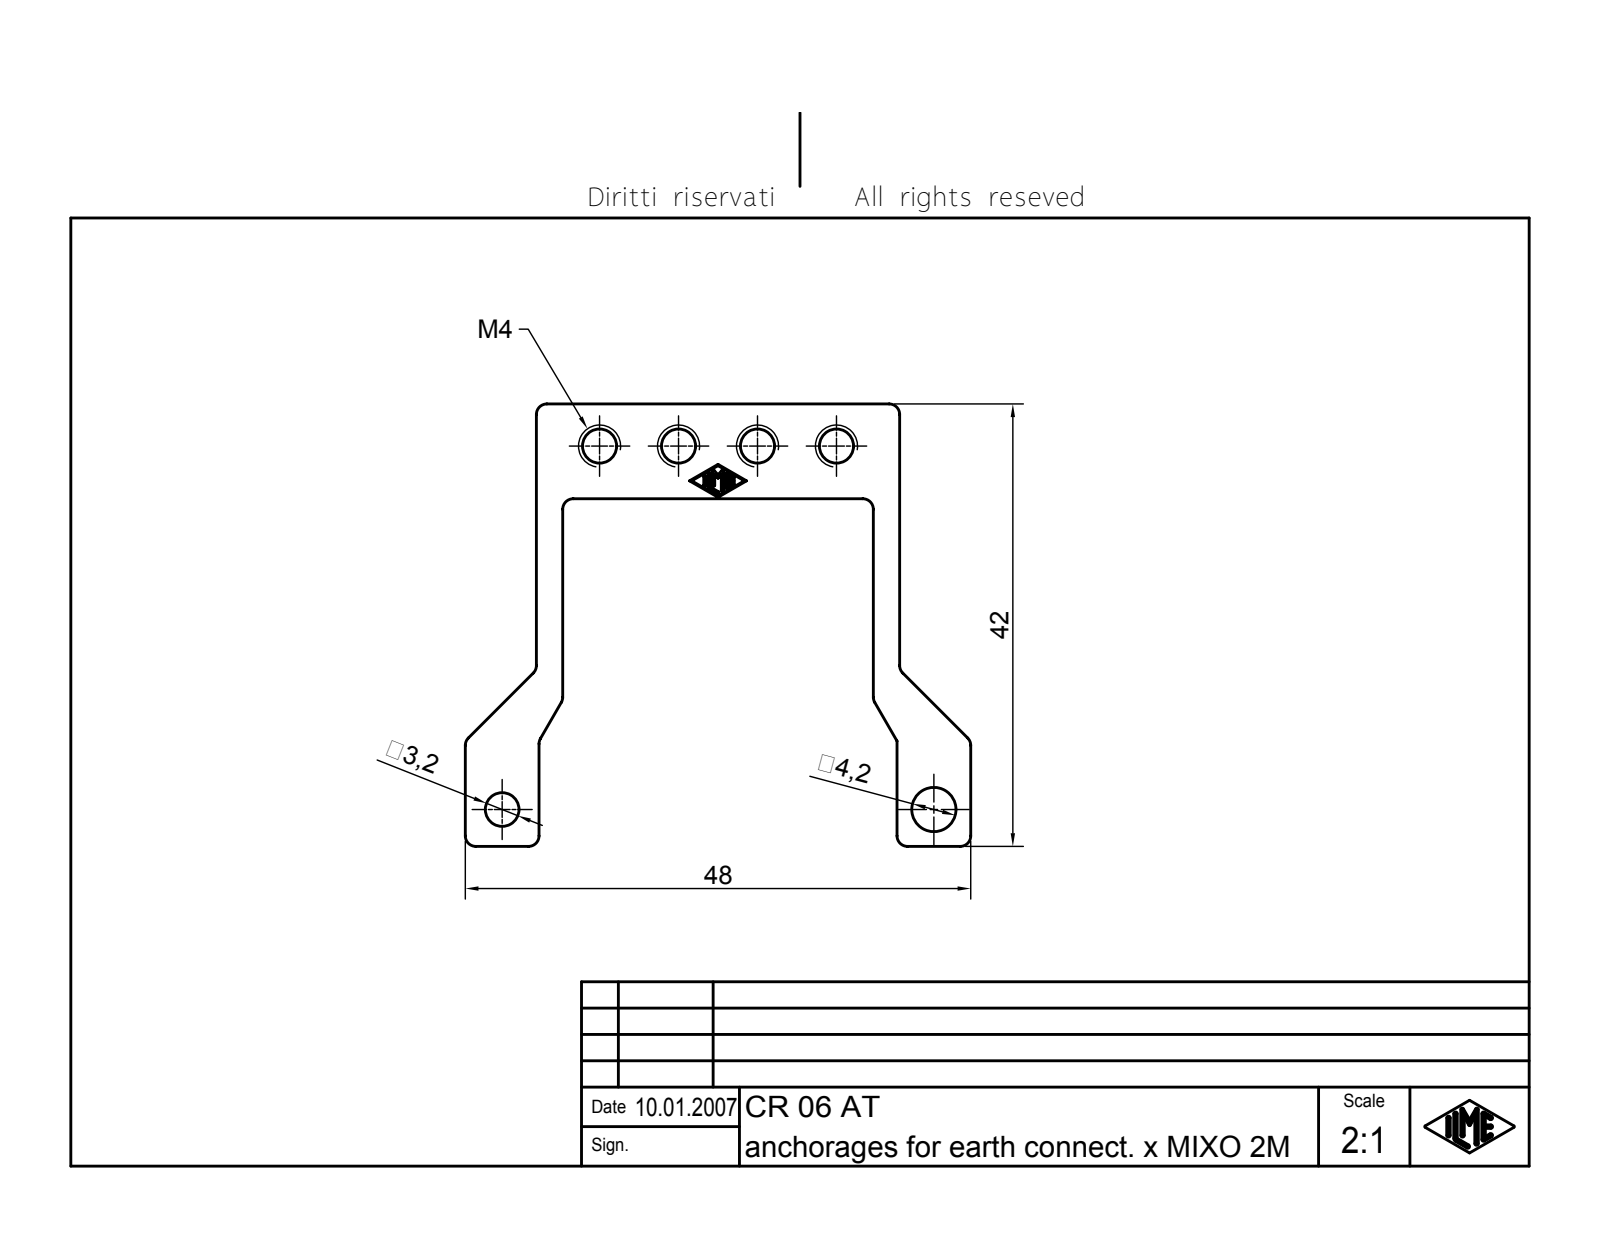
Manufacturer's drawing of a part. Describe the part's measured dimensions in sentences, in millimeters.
The part is named "CR 06 AT". Its 3-D file was written by "Autodesk Inventor 7 (AUTOMOTIVE_DESIGN)". It is 1 solid with 111 faces: 55 planar, 48 cylindrical and 8 other. Overall it measures 48 by 42 by 2 millimeters. Its volume is 1 092 cubic millimeters and its surface area 1 693 square millimeters. Round holes: 1 of diameter 3.2, 1 of diameter 4.2. Partial cylindrical surfaces (rounded edges, fillets, slot ends): 15 of radius 1, 14 of radius 0.1. The main face-to-face distances are 2, 2.5, 32, 9, 34.5, 29.5, 34.25, 2.25, 31.75, 6.75. The hole center spacings are 41.
